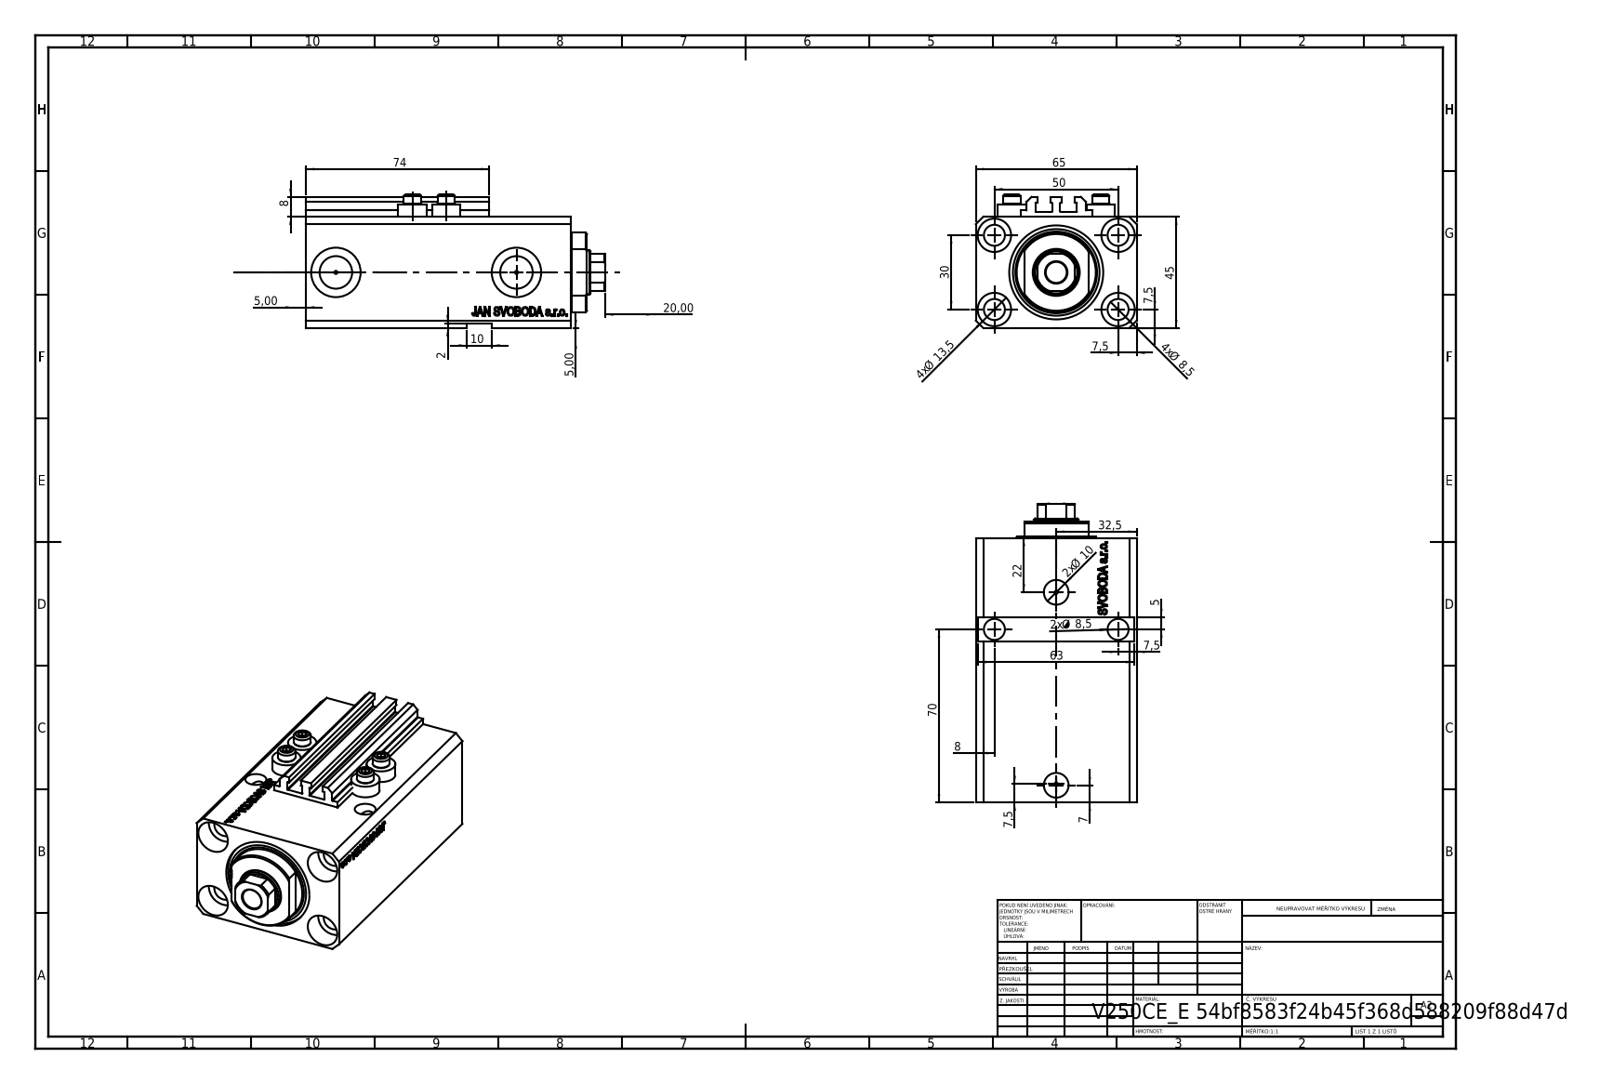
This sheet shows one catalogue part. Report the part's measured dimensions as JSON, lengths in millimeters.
{"part_name": "ALLEN BOLT V250CE; V250CE_E_Body; V250CE_C_VCP; V250CE_VC_E", "step_written_by": "SolidWorks 2019 (CONFIG_CONTROL_DESIGN)", "units": "millimeters", "bodies": {"solids": 8, "faces": 1067, "planar": 511, "cylindrical": 126, "other": 430}, "overall_size": [120.9, 65, 54], "volume_mm3": 276859, "surface_area_mm2": 77961, "round_holes": [[8.5, 7], [1.25, 4], [4, 4], [13.5, 4], [10, 2], [13.16, 2], [20, 2], [18, 1], [25, 1], [38, 1]], "round_bosses_or_shafts": [[11.6, 4], [7, 4]], "partial_cylinders_radius": [[0.2, 10], [8.5, 1], [16, 1]], "face_to_face_distances": [45, 65, 81.9, 2, 47, 107, 25.1, 2.5, 6.9, 75], "hole_center_spacings": [29.15, 50, 13.6, 15.12, 27.89, 30, 33.62, 36]}
